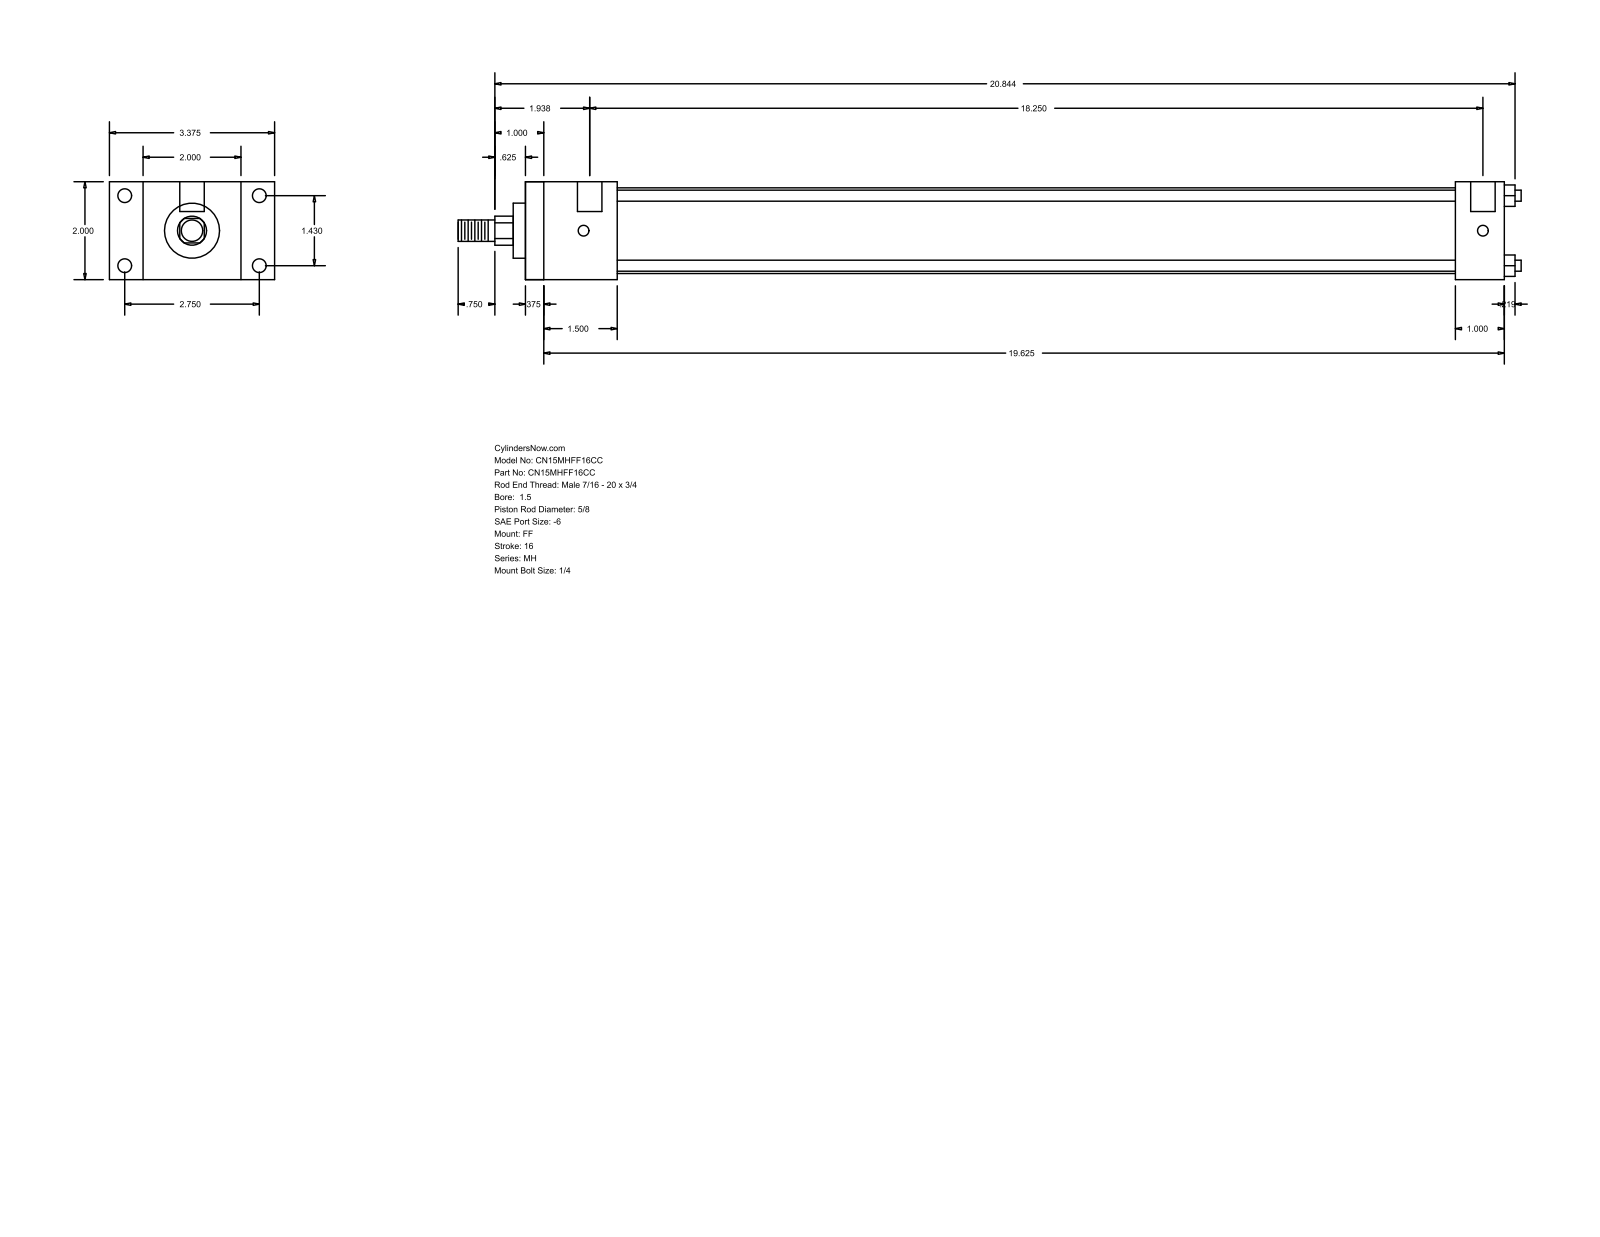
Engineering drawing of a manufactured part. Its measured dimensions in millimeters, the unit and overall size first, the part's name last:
Units: millimetres
Overall size (bounding box): 551.66 × 85.72 × 50.8
Round holes (diameter × count): ⌀5.56 ×4, ⌀7.14 ×4, ⌀12.7 ×2
Round bosses / shafts (diameter × count): ⌀5.71 ×4, ⌀44.45 ×1, ⌀28.57 ×1, ⌀15.88 ×1, ⌀11.11 ×1
Partial cylindrical surfaces — rounded edges, fillets, slot ends (radius × count): R7.54 ×1
Main face-to-face distances: 50.8, 508, 498.48, 9.52, 25.4, 17.46, 68.26, 47.62, 38.1, 460.38
Hole centre spacings: 36.32, 69.84, 78.72, 466.72, 3.17, 463.55
Bodies: 0 solids, 92 faces (64 planar, 28 cylindrical, 0 other)
Part name (STEP PRODUCT): MH_FF__0150_0.625
STEP written by: GSSL Pune (CONFIG_CONTROL_DESIGN)
